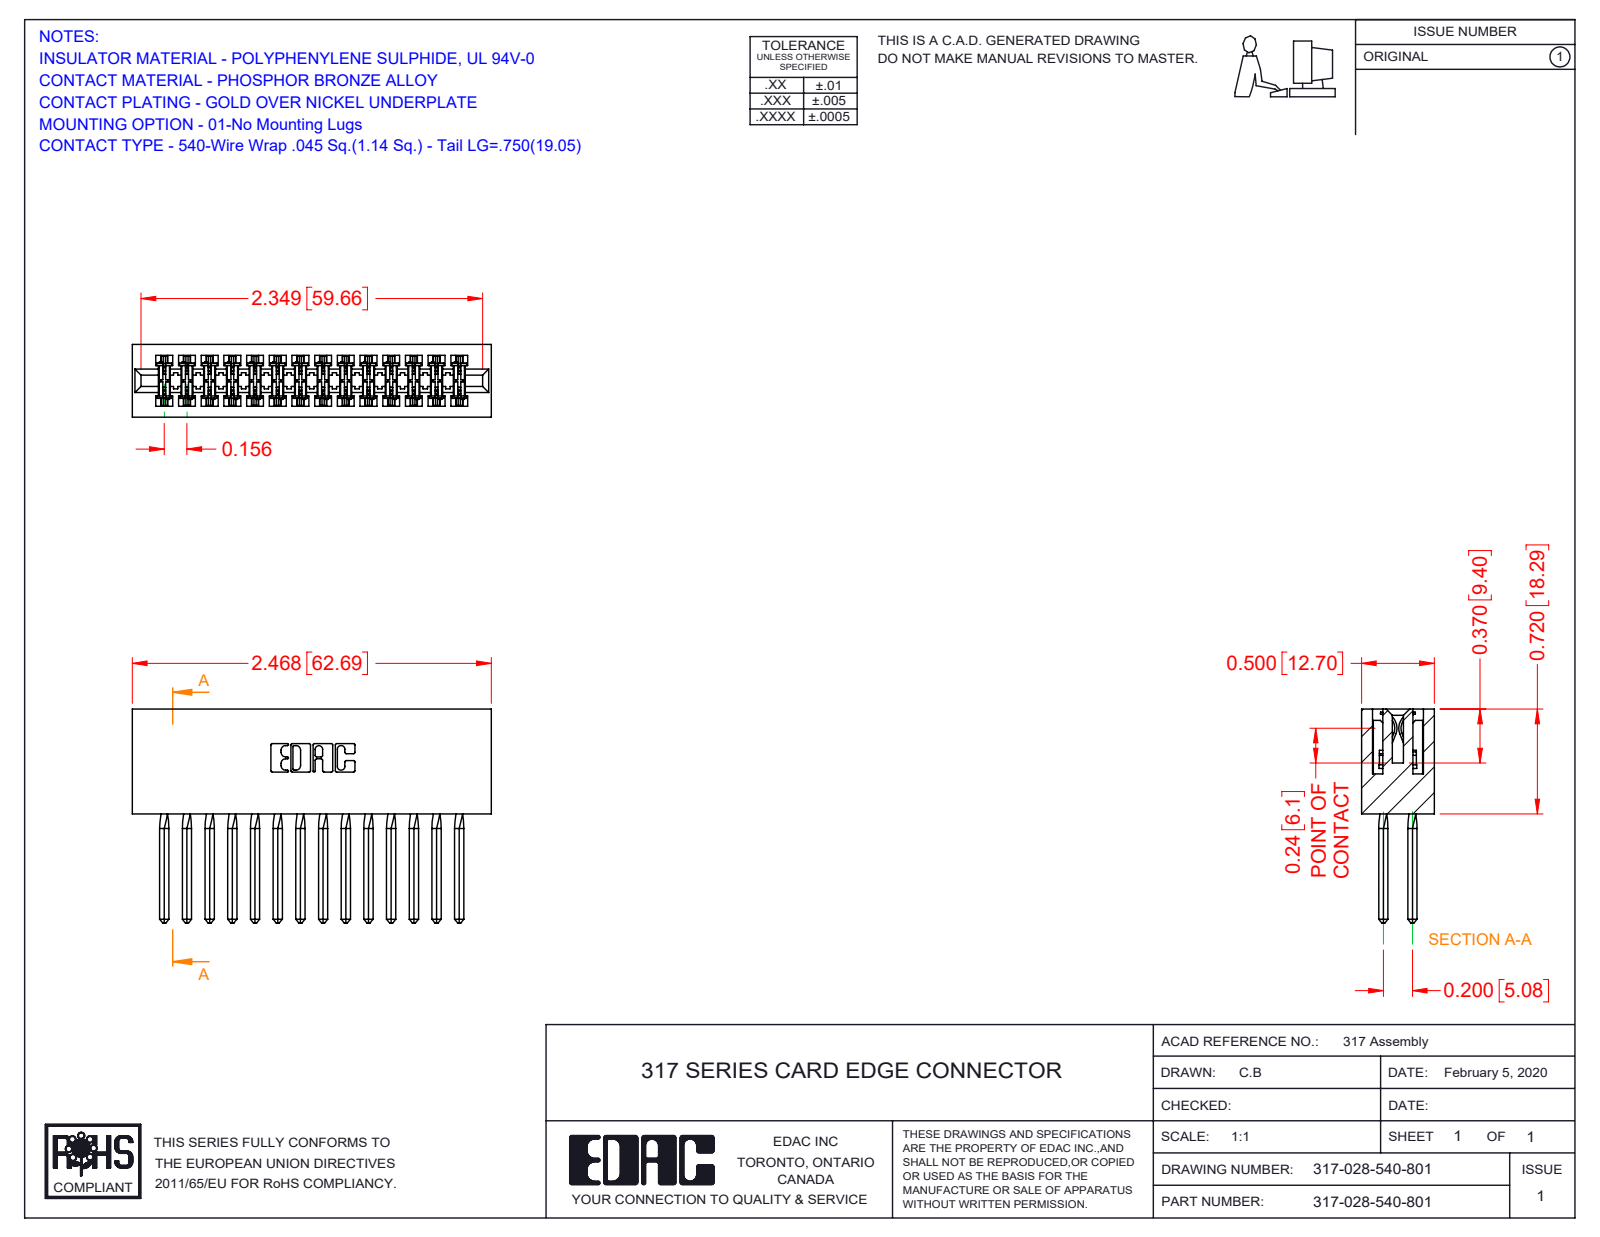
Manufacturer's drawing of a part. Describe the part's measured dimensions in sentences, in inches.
The part is named "317 Part_Lugless; 317-290-001_540; 317-028-540-801". Its 3-D file was written by "SolidWorks 2016 (CONFIG_CONTROL_DESIGN)". It is 29 solids with 2582 faces: 2094 planar, 376 cylindrical and 112 other. Overall it measures 2.468 by 1.47 by 0.5 inches. Its volume is 0.694 cubic inches and its surface area 25.03 square inches. Partial cylindrical surfaces (rounded edges, fillets, slot ends): 56 of radius 0.015, 22 of radius 0.01, 6 of radius 0.007, 6 of radius 0.031, 3 of radius 0.026, 2 of radius 0.095, 2 of radius 0.1, 2 of radius 0.11. The main face-to-face distances are 0.5, 0.075, 0.425, 0.11, 0.35, 0.22, 0.156, 0.116, 0.72, 0.195.
